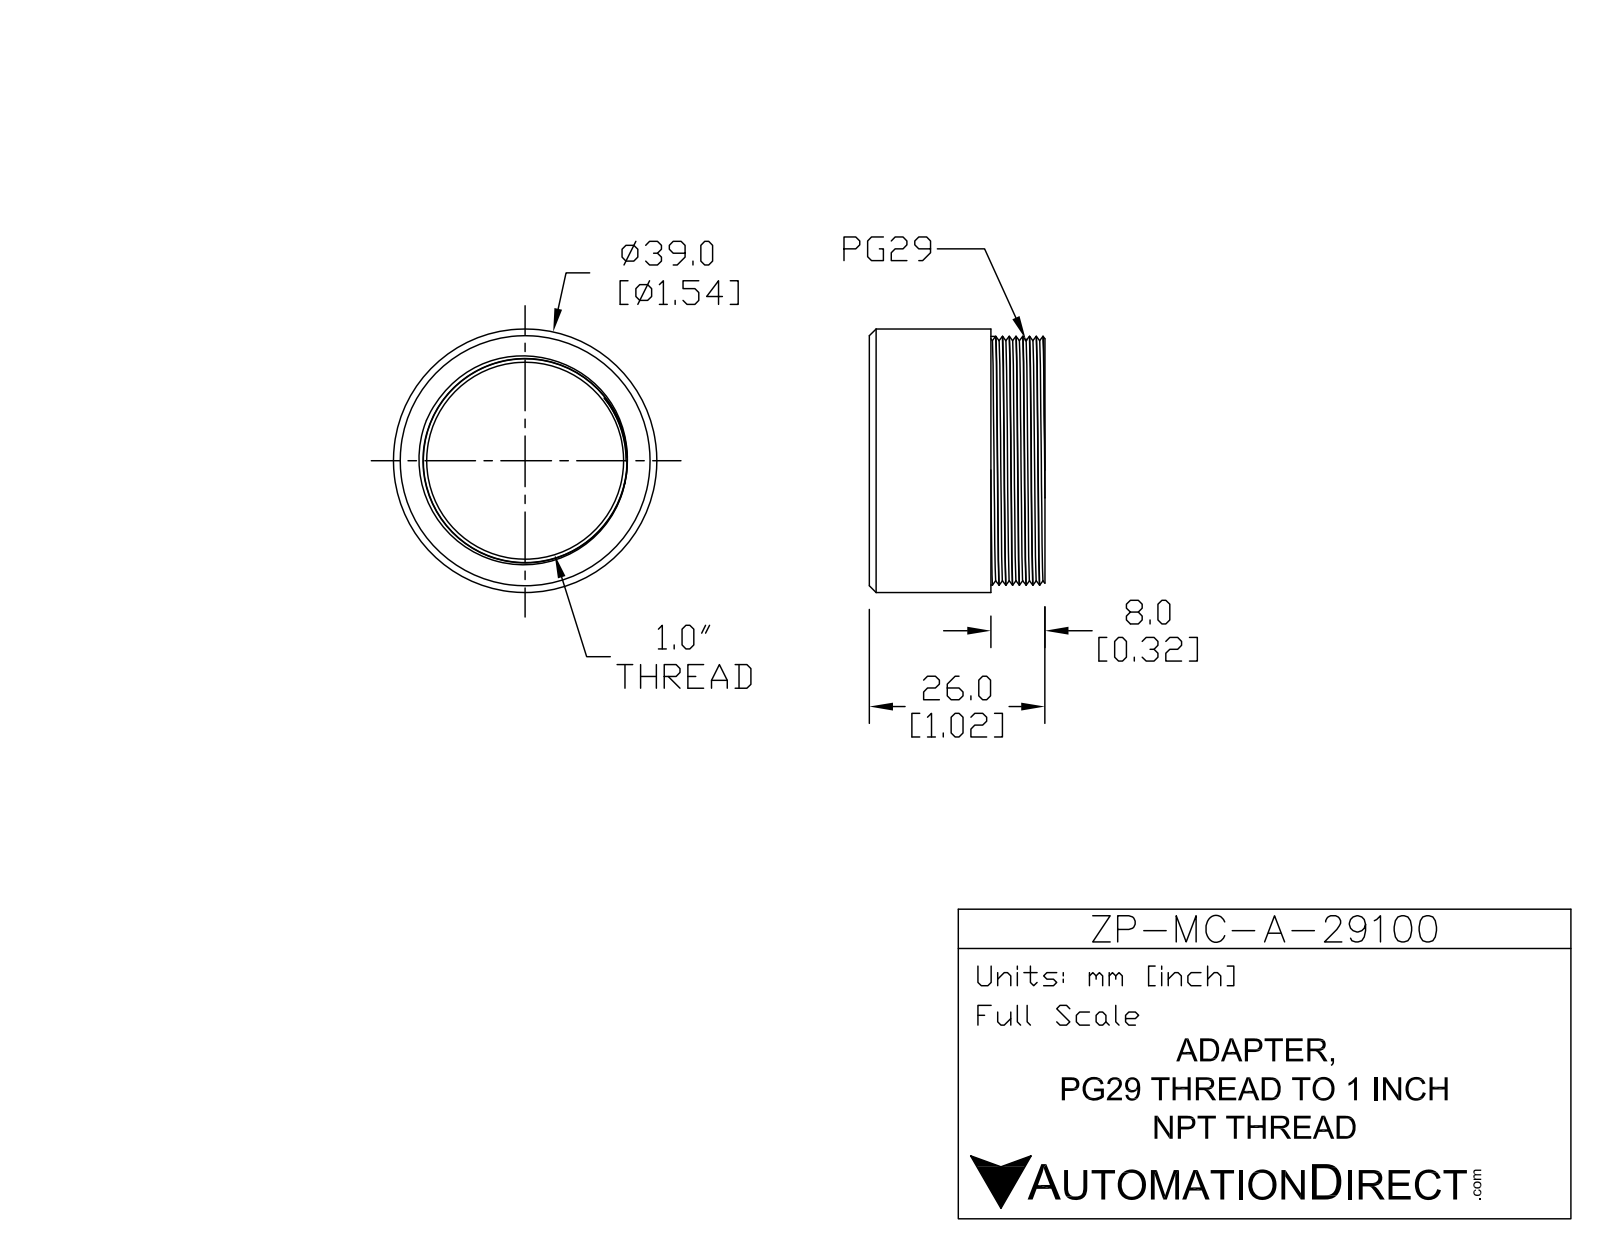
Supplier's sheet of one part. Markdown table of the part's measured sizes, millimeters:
| quantity | value |
| --- | --- |
| part name | ZP-MC-A-29100 |
| STEP written by | SolidWorks 2011 (AUTOMOTIVE_DESIGN) |
| units | millimeters |
| bodies | 1 solid, 17 faces (6 planar, 5 cylindrical, 6 other) |
| overall size | 39 × 39 × 26 |
| volume | 11 251 mm³ |
| surface area | 7 851 mm² |
| round holes (diameter × count) | 29.15 × 1, 30.15 × 1 |
| round bosses / shafts (diameter × count) | 39 × 1, 36.8 × 1 |
| partial cylindrical surfaces (radius × count) | 14.95 × 1 |
| main face-to-face distances | 26, 8, 18, 13, 5 |
